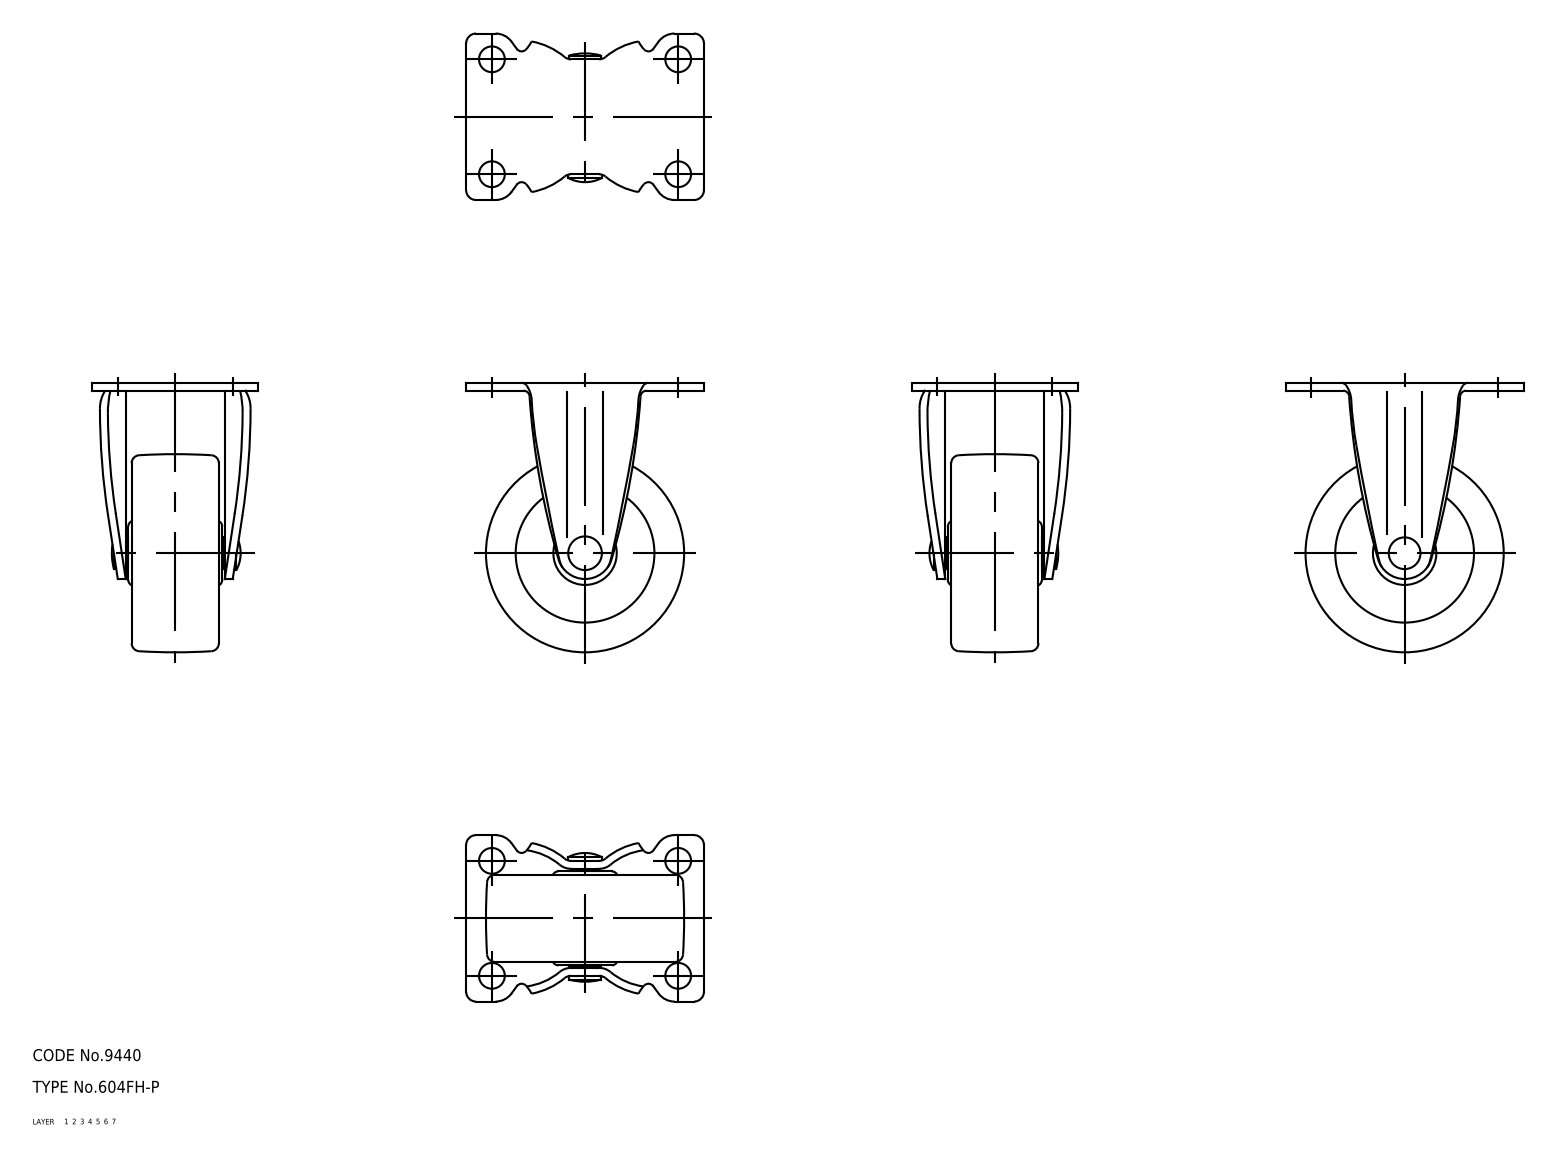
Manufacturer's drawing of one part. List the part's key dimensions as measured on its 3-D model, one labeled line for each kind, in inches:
Part name (STEP PRODUCT): wheel; axle; No_604FH_P_14293_36
STEP written by: CADfix (AUTOMOTIVE_DESIGN)
Units: inches
Bodies: 3 solids, 156 faces (0 planar, 0 cylindrical, 156 other)
Overall size (bounding box): 2.677 × 2.362 × 1.654
Volume: 2.682 in³ · Surface area: 28.67 in²
